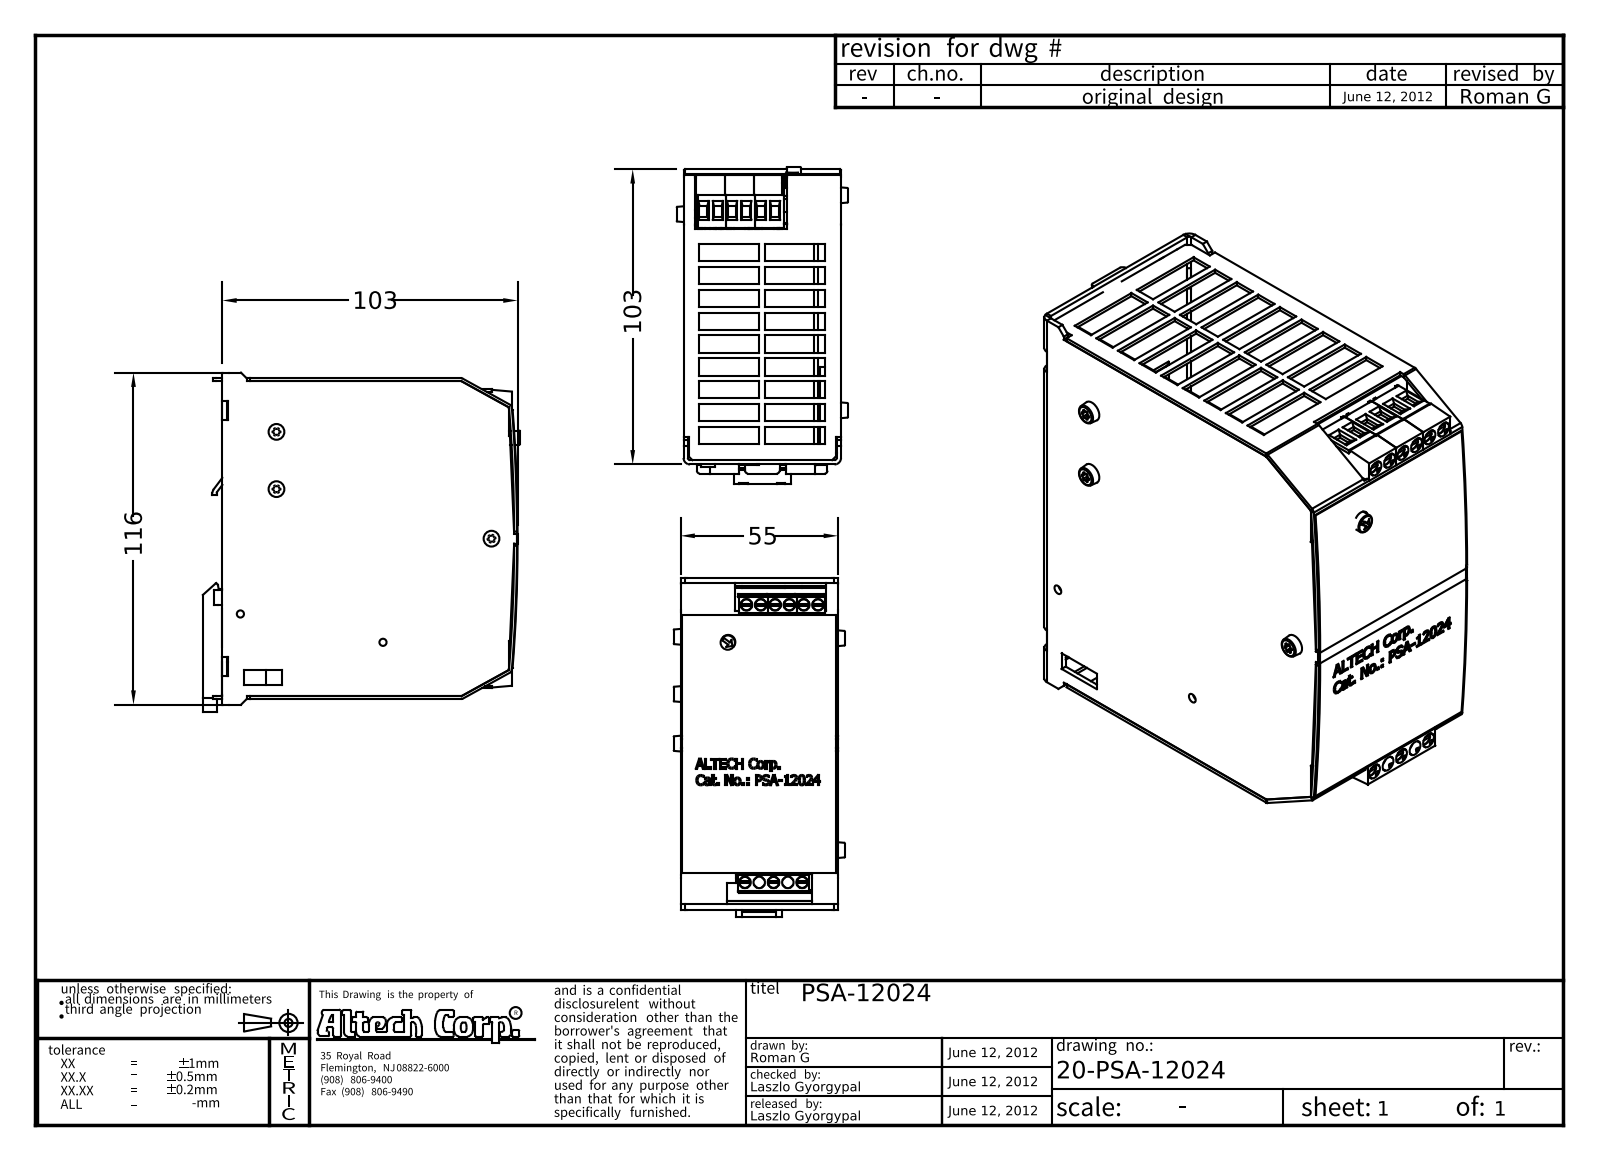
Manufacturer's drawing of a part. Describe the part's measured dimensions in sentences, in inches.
The part is named "ALTECH-PSA-12024". Its 3-D file was written by "Autodesk Inventor 2013 (CONFIG_CONTROL_DESIGN)". It is 1 solid with 2147 faces: 1524 planar, 399 cylindrical and 224 other. Overall it measures 4.671 by 4.354 by 2.354 inches. Its volume is 5.765 cubic inches and its surface area 183.7 square inches. Round holes: 38 of diameter 0.039, 11 of diameter 0.157, 4 of diameter 0.035, 4 of diameter 0.091, 3 of diameter 0.11, 3 of diameter 0.13, 2 of diameter 0.079, 2 of diameter 0.098, 2 of diameter 0.122. Round bosses or shafts: 9 of diameter 0.152, 9 of diameter 0.055, 5 of diameter 0.118, 5 of diameter 0.105, 2 of diameter 0.185, 2 of diameter 0.06, 1 of diameter 0.354, 1 of diameter 0.197. Partial cylindrical surfaces (rounded edges, fillets, slot ends): 46 of radius 0.004, 31 of radius 0.01, 30 of radius 0.022, 17 of radius 0.02, 16 of radius 0.008, 12 of radius 0.047, 8 of radius 0.039, 8 of radius 0.059. The main face-to-face distances are 0.059, 2.106, 0.063, 2.165, 0.315, 0.311, 1.795, 1.854, 0.374, 1.732. The hole center spacings are 0.197, 0.1, 3.716, 0.394, 0.591, 3.817, 3.821, 3.823.
